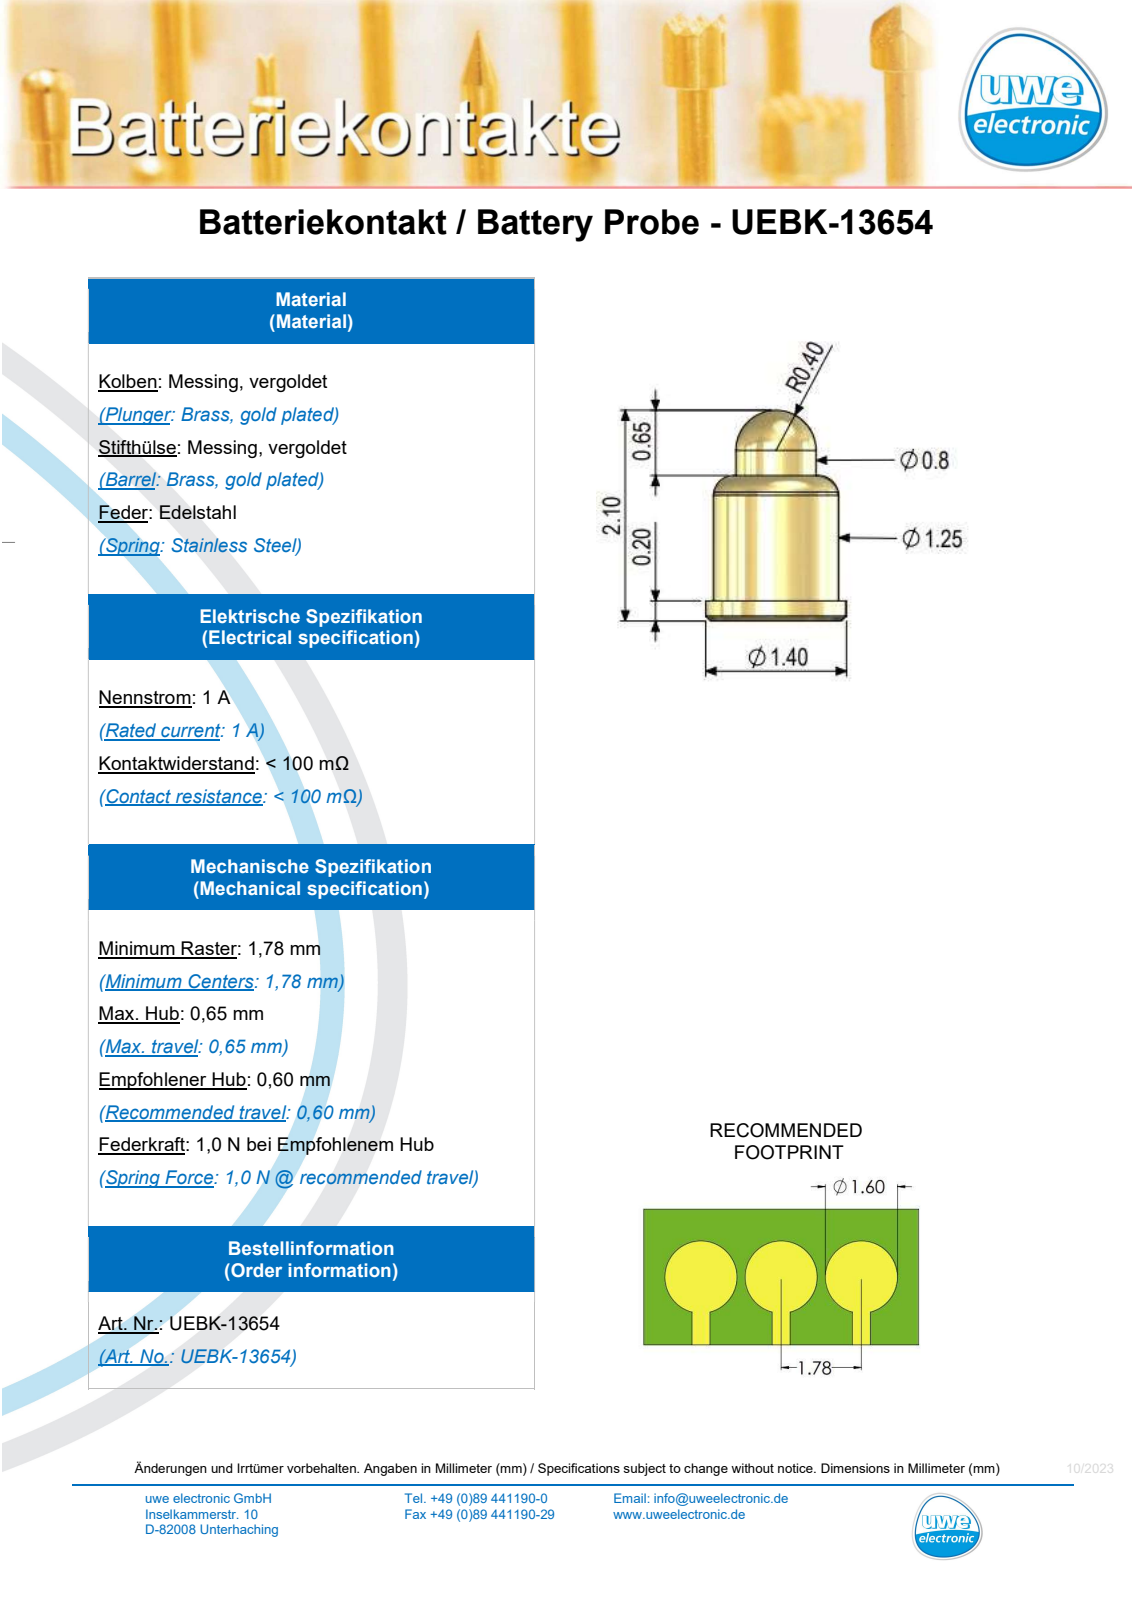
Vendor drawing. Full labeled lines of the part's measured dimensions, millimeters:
Part name (STEP PRODUCT): UEBK-13654_step
STEP written by: SolidWorks 2022 (AUTOMOTIVE_DESIGN)
Units: millimetres
Bodies: 1 solid, 16 faces (3 planar, 6 cylindrical, 7 other)
Overall size (bounding box): 2.1 × 1.4 × 1.4
Volume: 2 mm³ · Surface area: 10 mm²
Round bosses / shafts (diameter × count): ⌀1.4 ×1, ⌀1.25 ×1, ⌀0.8 ×1
Main face-to-face distances: 1.25, 1.45
